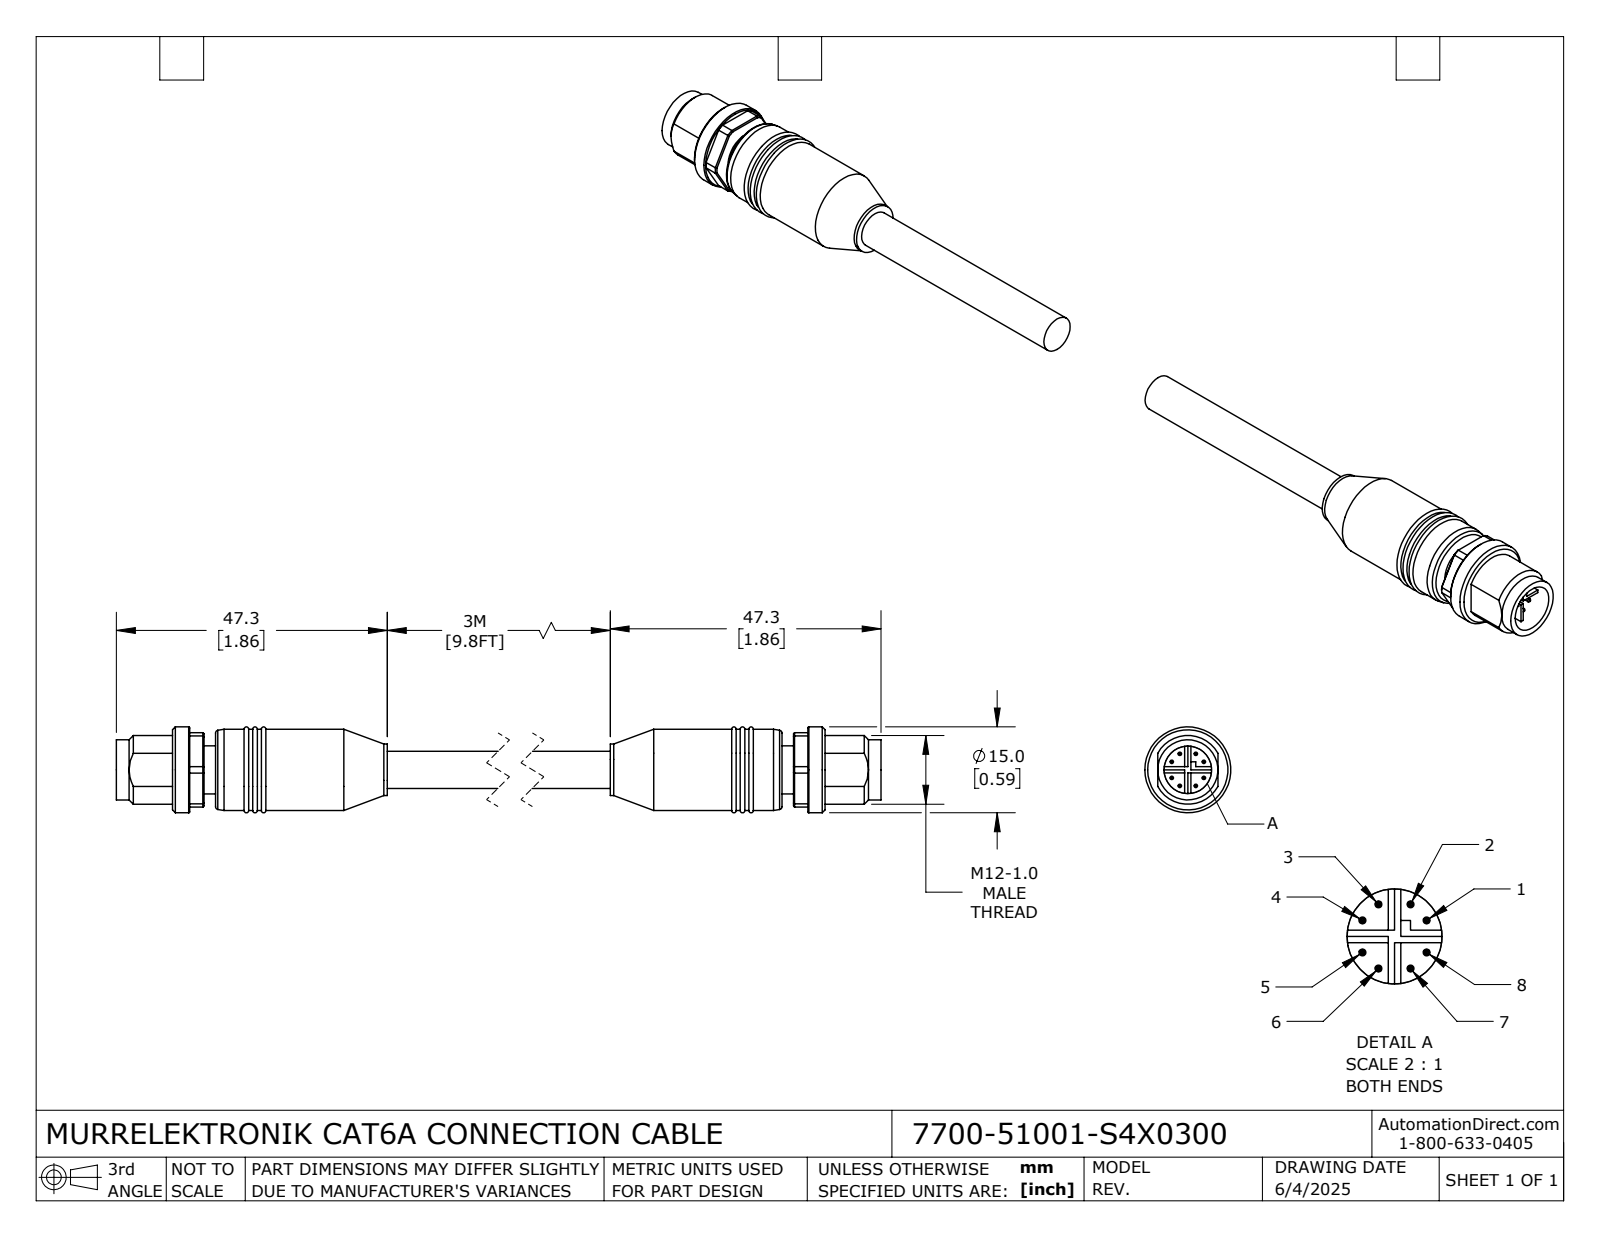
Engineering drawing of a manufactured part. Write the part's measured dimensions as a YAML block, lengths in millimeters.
part_name: "7700-51001-S4X0300_MALE; 7700-51001-S4X0300"
step_written_by: "SolidWorks 2024 (CONFIG_CONTROL_DESIGN)"
units: millimeters
bodies: {solids: 2, faces: 282, planar: 112, cylindrical: 88, other: 82}
overall_size: [209.6, 15, 15]
volume: 14953
surface_area: 7635
round_holes:
  - {diameter: 8.3, count: 1}
round_bosses_or_shafts:
  - {diameter: 0.6, count: 8}
  - {diameter: 15, count: 1}
  - {diameter: 14.2, count: 1}
  - {diameter: 10.5, count: 1}
  - {diameter: 9, count: 1}
  - {diameter: 8.4, count: 1}
  - {diameter: 6.5, count: 1}
partial_cylinders:
  - {radius: 6, count: 1}
  - {radius: 7.2, count: 1}
face_to_face_distances: [4.7, 5.8, 2, 177, 1.1, 5.5, 13, 7.5, 182.5, 184.5]
